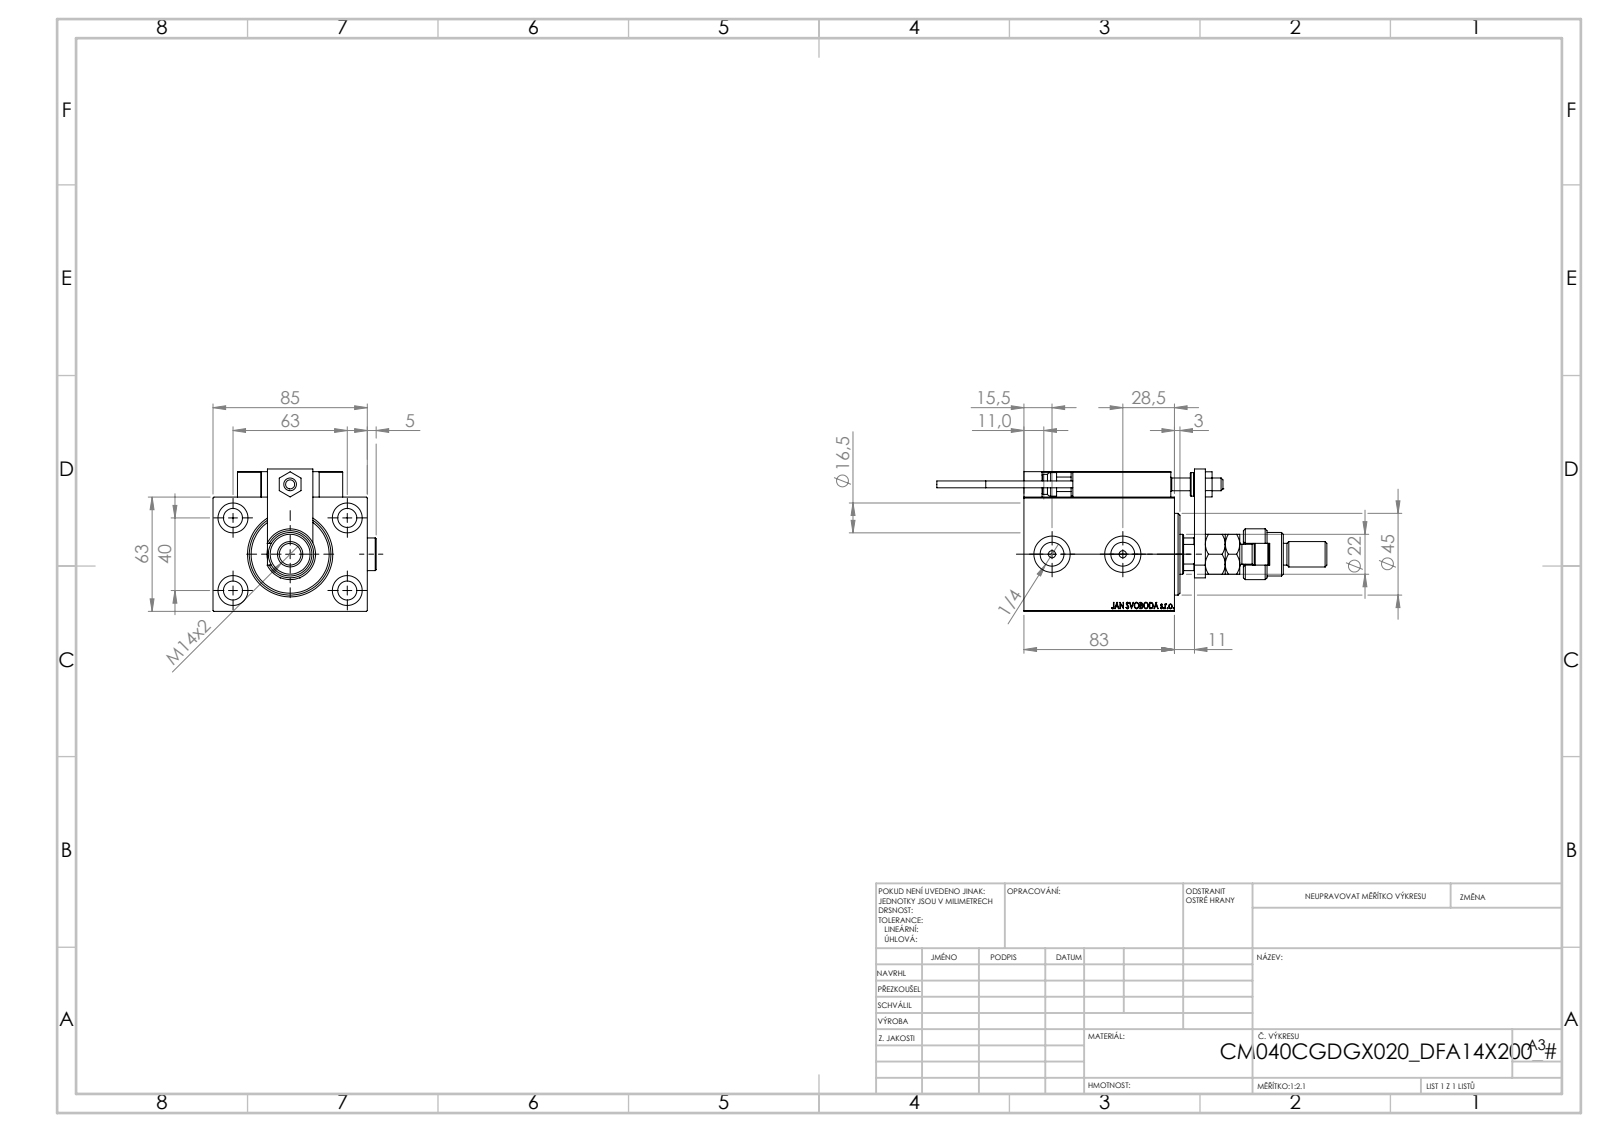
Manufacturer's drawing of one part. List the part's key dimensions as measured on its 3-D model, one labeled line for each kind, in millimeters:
Part name (STEP PRODUCT): ALLEN BOLT D5; Zatka_OIL_PORT; Block; V450CM_VC_B (+8 more)
STEP written by: SolidWorks 2019 (CONFIG_CONTROL_DESIGN)
Units: millimetres
Bodies: 27 solids, 1419 faces (622 planar, 215 cylindrical, 582 other)
Overall size (bounding box): 215 × 89.9 × 78.5
Volume: 464 723 mm³ · Surface area: 106 968 mm²
Round holes (diameter × count): ⌀4 ×6, ⌀8 ×5, ⌀16.5 ×5, ⌀3.2 ×4, ⌀10.5 ×4, ⌀5 ×2, ⌀13.16 ×2, ⌀20 ×2, ⌀7 ×1, ⌀12.5 ×1, ⌀22 ×1, ⌀25.5 ×1
Round bosses / shafts (diameter × count): ⌀18 ×3, ⌀11 ×2, ⌀5 ×2, ⌀3.8 ×2, ⌀28 ×1, ⌀24 ×1, ⌀14 ×1, ⌀13 ×1
Partial cylindrical surfaces — rounded edges, fillets, slot ends (radius × count): R0.3 ×30, R3 ×2, R9.75 ×1, R10.5 ×1
Main face-to-face distances: 63, 85, 14, 83, 32, 51, 11, 22, 17, 51.4
Hole centre spacings: 37.31, 11.37, 20, 29.59, 29.69, 35.06, 36.06, 36.53
